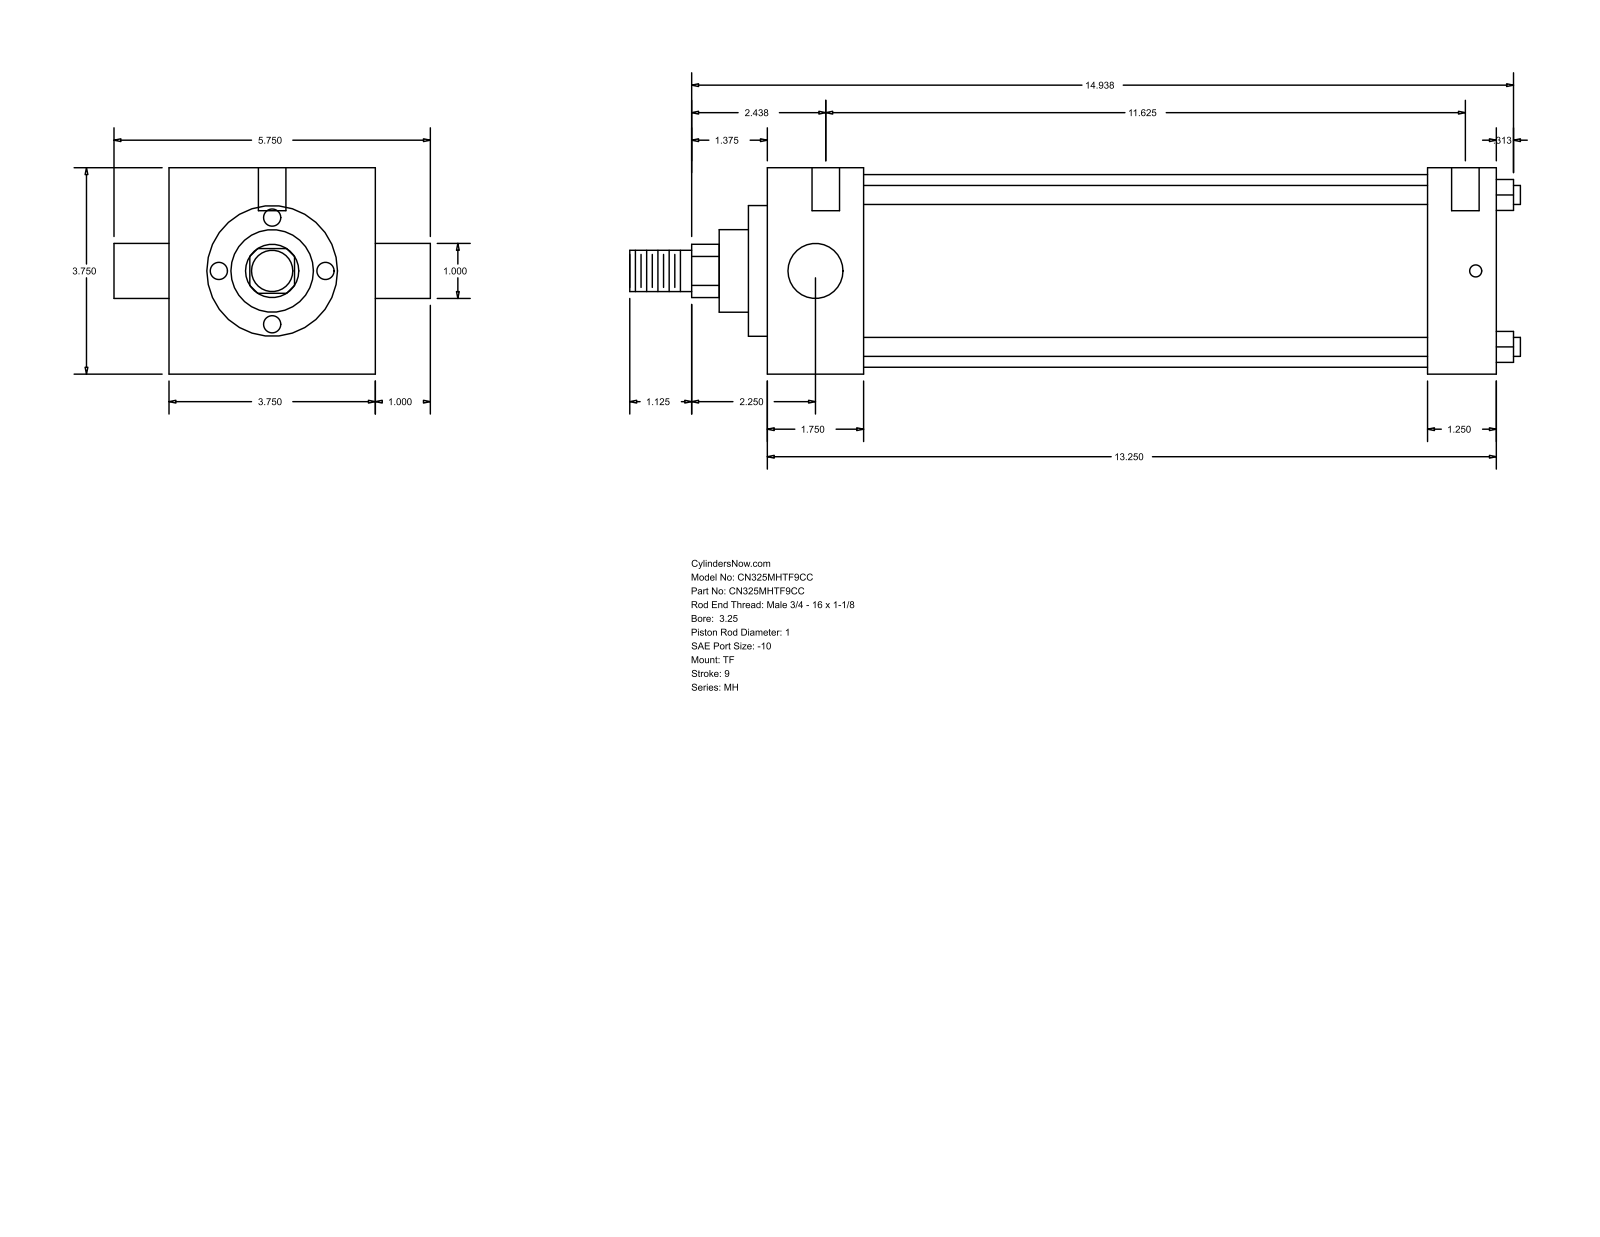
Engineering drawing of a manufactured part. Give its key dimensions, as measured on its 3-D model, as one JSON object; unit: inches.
{"part_name": "MH_TF__0325_1", "step_written_by": "GSSL Pune (CONFIG_CONTROL_DESIGN)", "units": "inches", "bodies": {"solids": 0, "faces": 86, "planar": 61, "cylindrical": 25, "other": 0}, "overall_size": [16.187, 5.75, 3.75], "round_holes": [[0.219, 3], [0.5, 2]], "round_bosses_or_shafts": [[0.345, 4], [1, 2], [3.5, 1], [2.375, 1], [1.5, 1], [0.75, 1]], "partial_cylinders_radius": [[0.484, 1]], "face_to_face_distances": [3.75, 13.25, 1.75, 12, 10.25, 11.5, 1.25, 0.344, 2.094, 12.344], "hole_center_spacings": [0.062, 0.187, 11.625, 11.687, 11.813, 11.875]}
